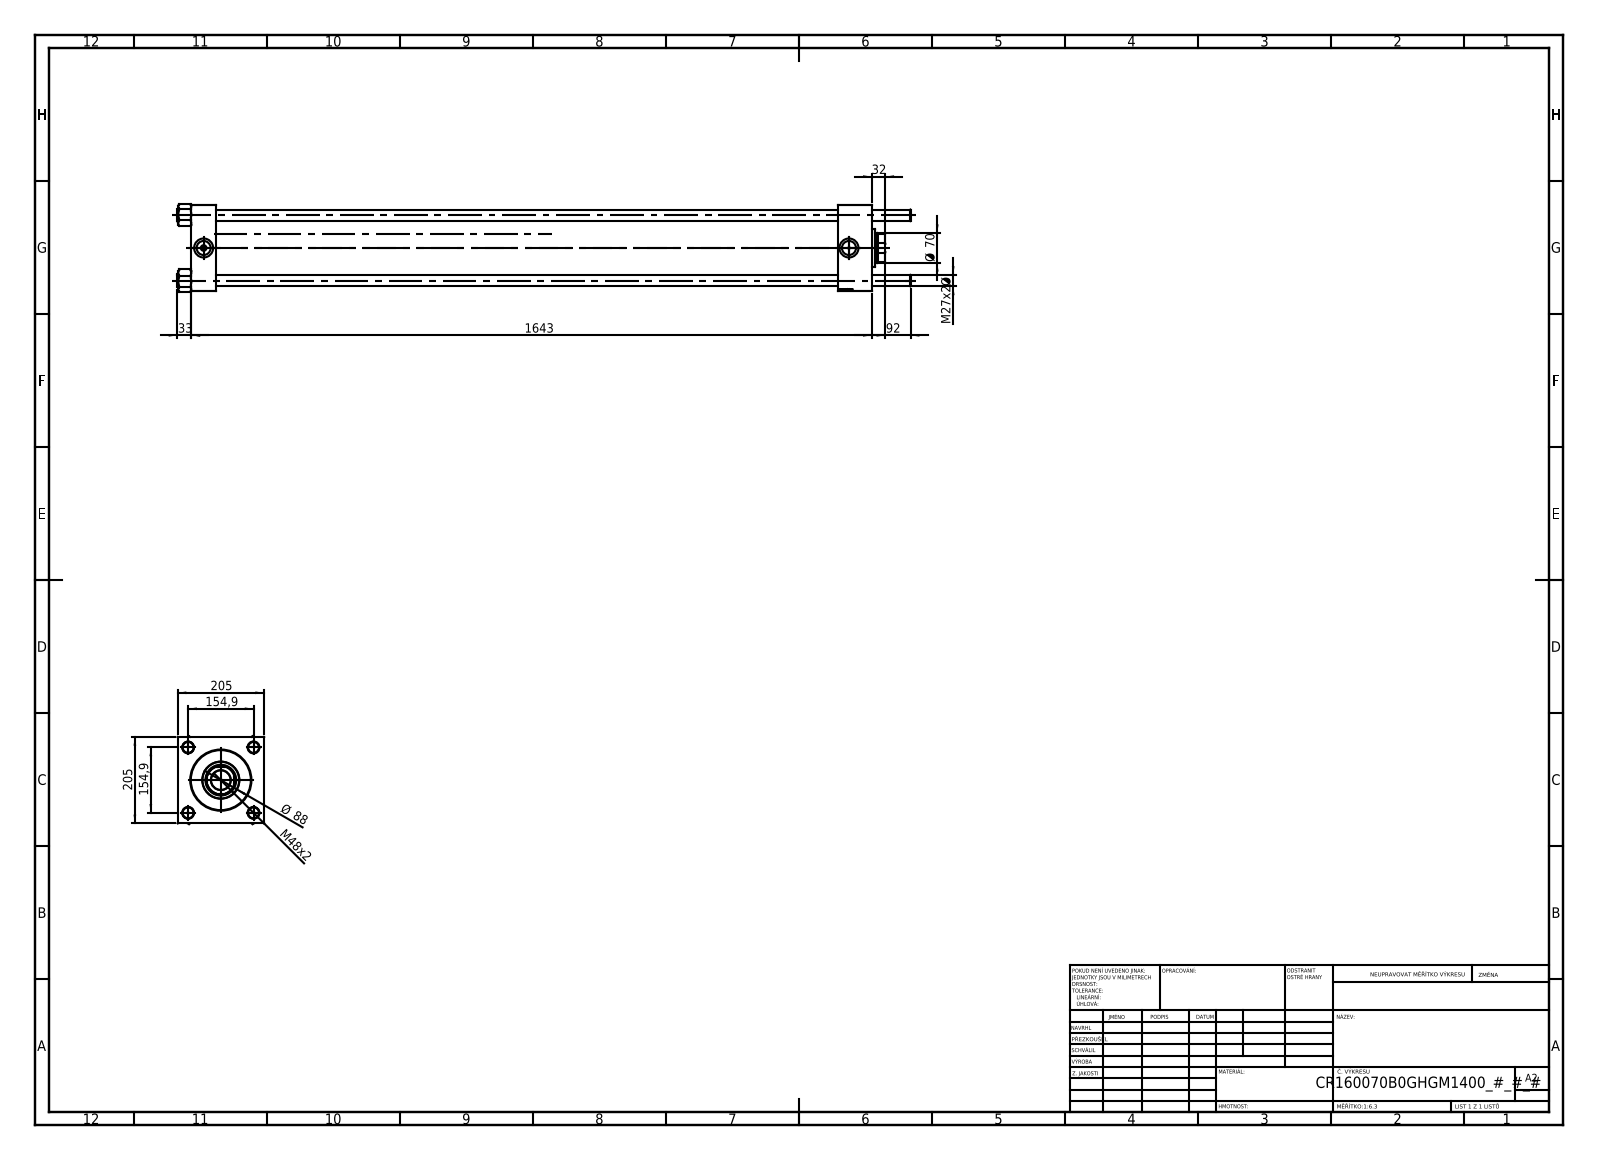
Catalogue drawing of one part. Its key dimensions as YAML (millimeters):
part_name: "V215CR_VCP_B; V215CR_B-1; V215_VC_A; V215CR_B_TYCINKA (+1 more)"
step_written_by: "SolidWorks 2019 (CONFIG_CONTROL_DESIGN)"
units: millimeters
bodies: {solids: 11, faces: 1206, planar: 480, cylindrical: 78, other: 648}
overall_size: [1736, 207.94, 205]
volume: 18340000
surface_area: 2939000
round_holes:
  - {diameter: 27, count: 4}
  - {diameter: 7, count: 2}
  - {diameter: 33.24, count: 2}
  - {diameter: 45, count: 2}
  - {diameter: 46.5, count: 1}
  - {diameter: 70, count: 1}
  - {diameter: 73, count: 1}
  - {diameter: 120, count: 1}
  - {diameter: 142, count: 1}
  - {diameter: 160, count: 1}
round_bosses_or_shafts:
  - {diameter: 30, count: 4}
  - {diameter: 166, count: 1}
  - {diameter: 88, count: 1}
partial_cylinders:
  - {radius: 34, count: 1}
face_to_face_distances: [205, 58, 1611, 1553, 1530, 1472, 81, 1582.3, 1524.3, 52.3]
hole_center_spacings: [109.53, 154.9, 219.06, 1528]
